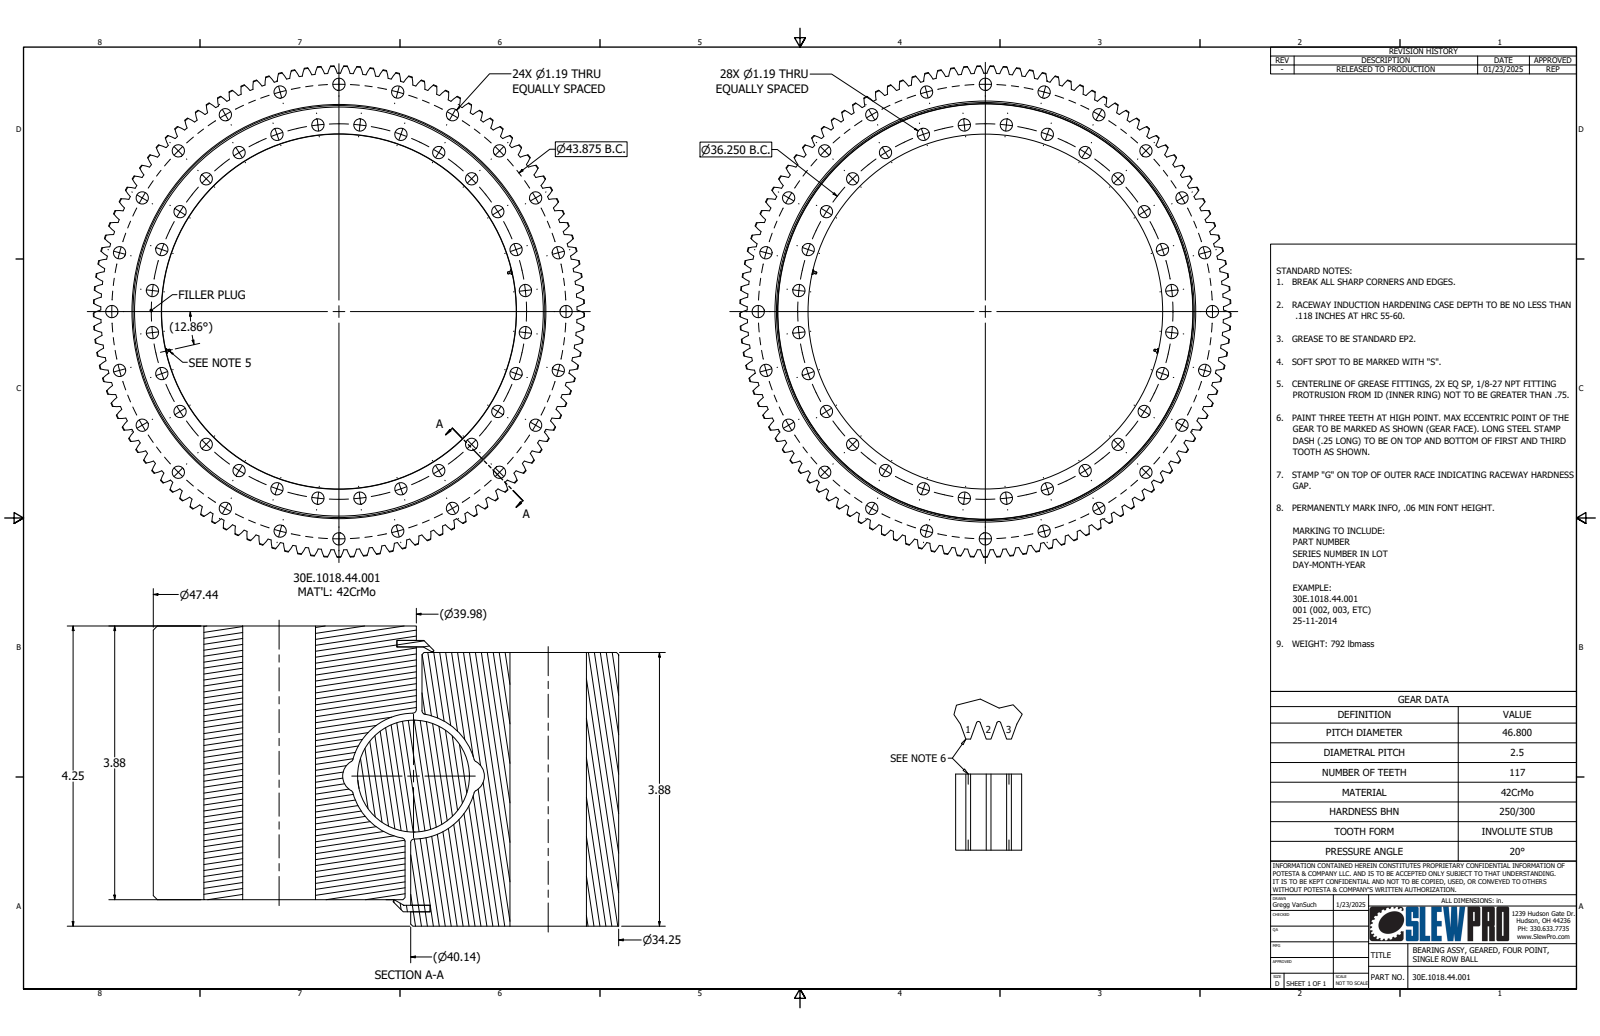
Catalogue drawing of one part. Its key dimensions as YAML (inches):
part_name: "30E.1018.44.001; 1_8 NPT Fitting; Spur Gears1"
step_written_by: "Autodesk Inventor 2024 (AUTOMOTIVE_DESIGN)"
units: inches
bodies: {solids: 8, faces: 1015, planar: 36, cylindrical: 540, other: 439}
overall_size: [47.439, 47.435, 4.25]
volume: 2792
surface_area: 5980
round_holes:
  - {diameter: 1.188, count: 52}
  - {diameter: 0.1, count: 2}
  - {diameter: 1.899, count: 1}
  - {diameter: 34.25, count: 1}
  - {diameter: 39.592, count: 1}
  - {diameter: 39.983, count: 1}
  - {diameter: 40.303, count: 1}
  - {diameter: 40.534, count: 1}
round_bosses_or_shafts:
  - {diameter: 40.533, count: 1}
  - {diameter: 40.143, count: 1}
  - {diameter: 39.823, count: 1}
  - {diameter: 39.591, count: 1}
  - {diameter: 1.897, count: 1}
partial_cylinders:
  - {radius: 4.164, count: 234}
  - {radius: 23, count: 1}
  - {radius: 23.72, count: 1}
face_to_face_distances: [3.875, 0.375, 4.25, 3.5, 3.75, 0.093, 0.204, 4.046, 0.171, 3.671]
hole_center_spacings: [30.694, 34.216, 35.341, 28.341, 8.067, 11.972, 15.728, 18.125]
